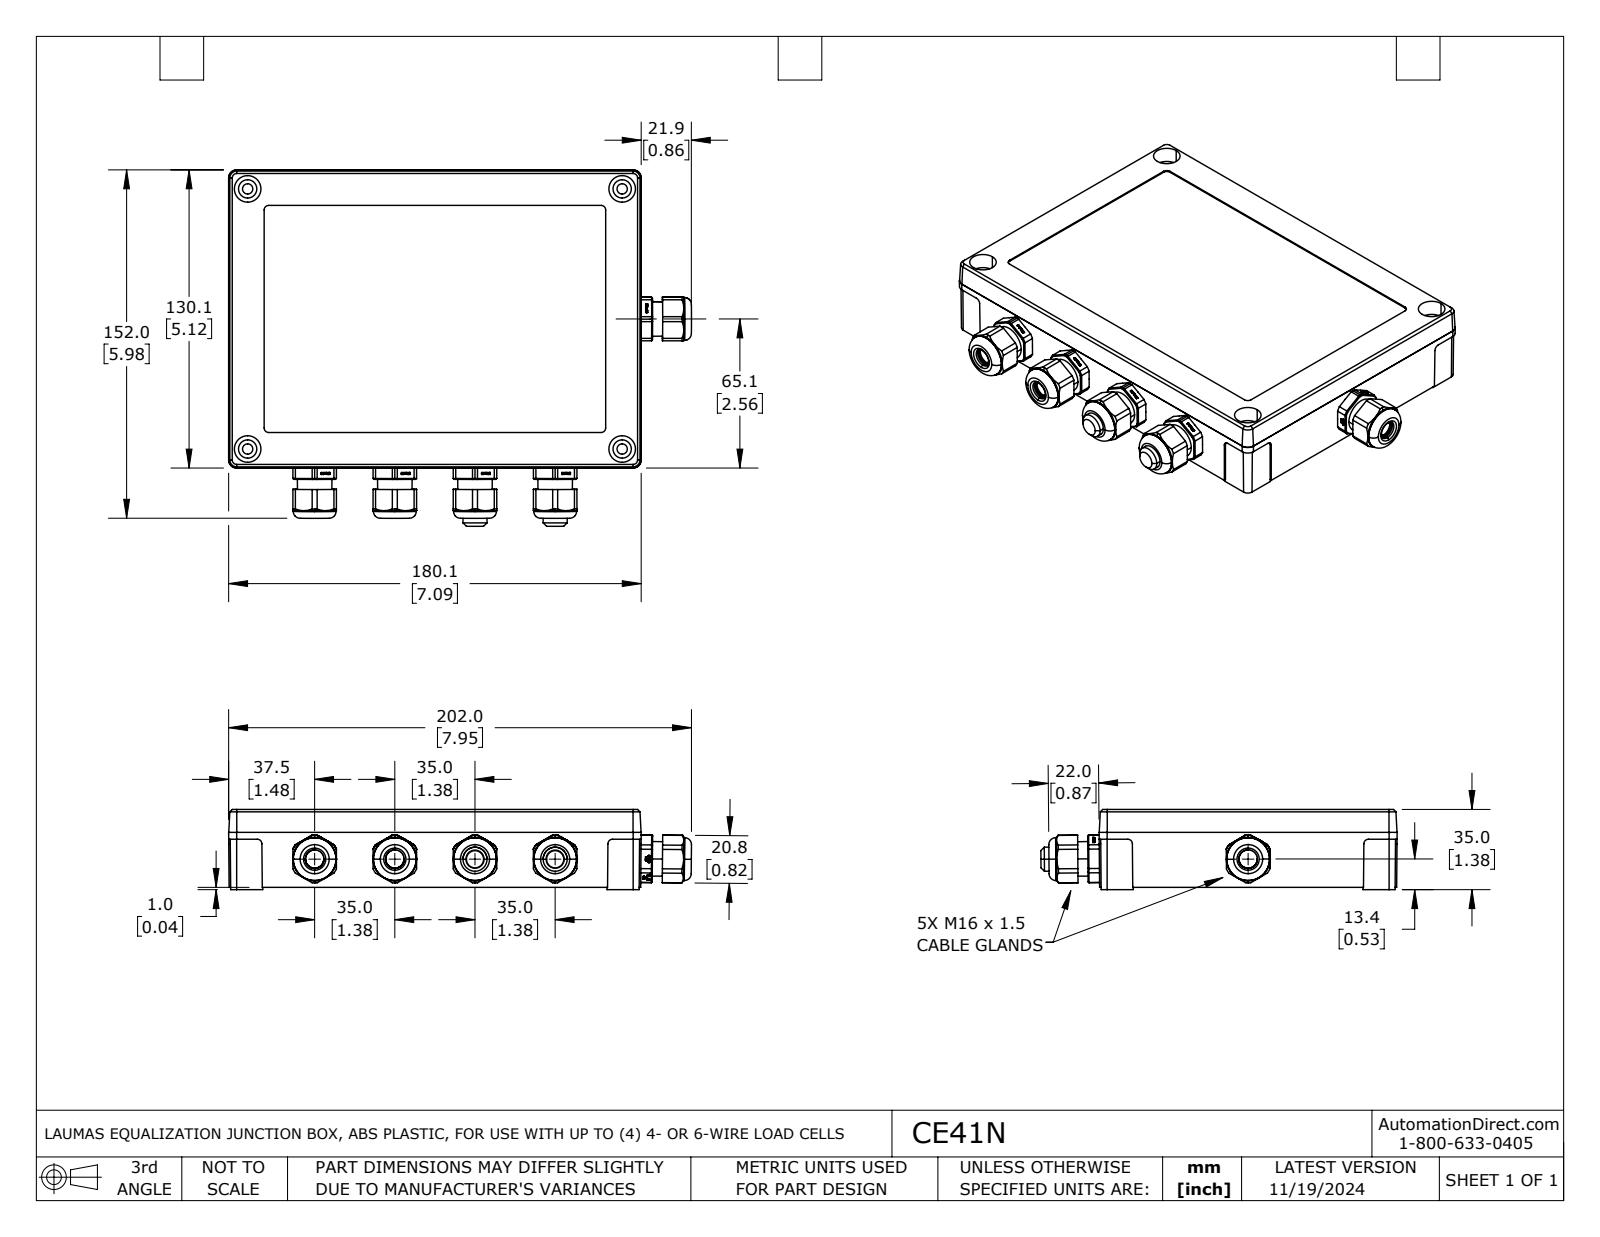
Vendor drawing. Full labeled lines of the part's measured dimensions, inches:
Part name (STEP PRODUCT): CE41N
STEP written by: SolidWorks 2021 (AUTOMOTIVE_DESIGN)
Units: inches
Bodies: 19 solids, 3280 faces (1660 planar, 1276 cylindrical, 344 other)
Overall size (bounding box): 7.955 × 6.123 × 1.378
Volume: 14.21 in³ · Surface area: 247.1 in²
Round holes (diameter × count): ⌀0.315 ×9, ⌀0.094 ×8, ⌀0.118 ×8, ⌀0.319 ×5, ⌀0.323 ×5, ⌀0.441 ×5, ⌀0.531 ×5, ⌀0.571 ×5, ⌀0.177 ×4, ⌀0.457 ×4, ⌀0.226 ×2
Round bosses / shafts (diameter × count): ⌀0.236 ×8, ⌀0.736 ×5, ⌀0.63 ×5, ⌀0.413 ×2, ⌀0.305 ×2
Partial cylindrical surfaces — rounded edges, fillets, slot ends (radius × count): R0.006 ×10, R0.006 ×10, R0.007 ×10, R0.008 ×10, R0.01 ×10, R0.011 ×10, R0.011 ×10, R0.012 ×10
Main face-to-face distances: 1.22, 0.118, 1.102, 1.319, 0.098, 1.201, 0.02, 1.339, 0.166, 0.276
Hole centre spacings: 1.378, 2.756, 1.333, 1.939, 1.969, 2.281, 3.252, 3.276
